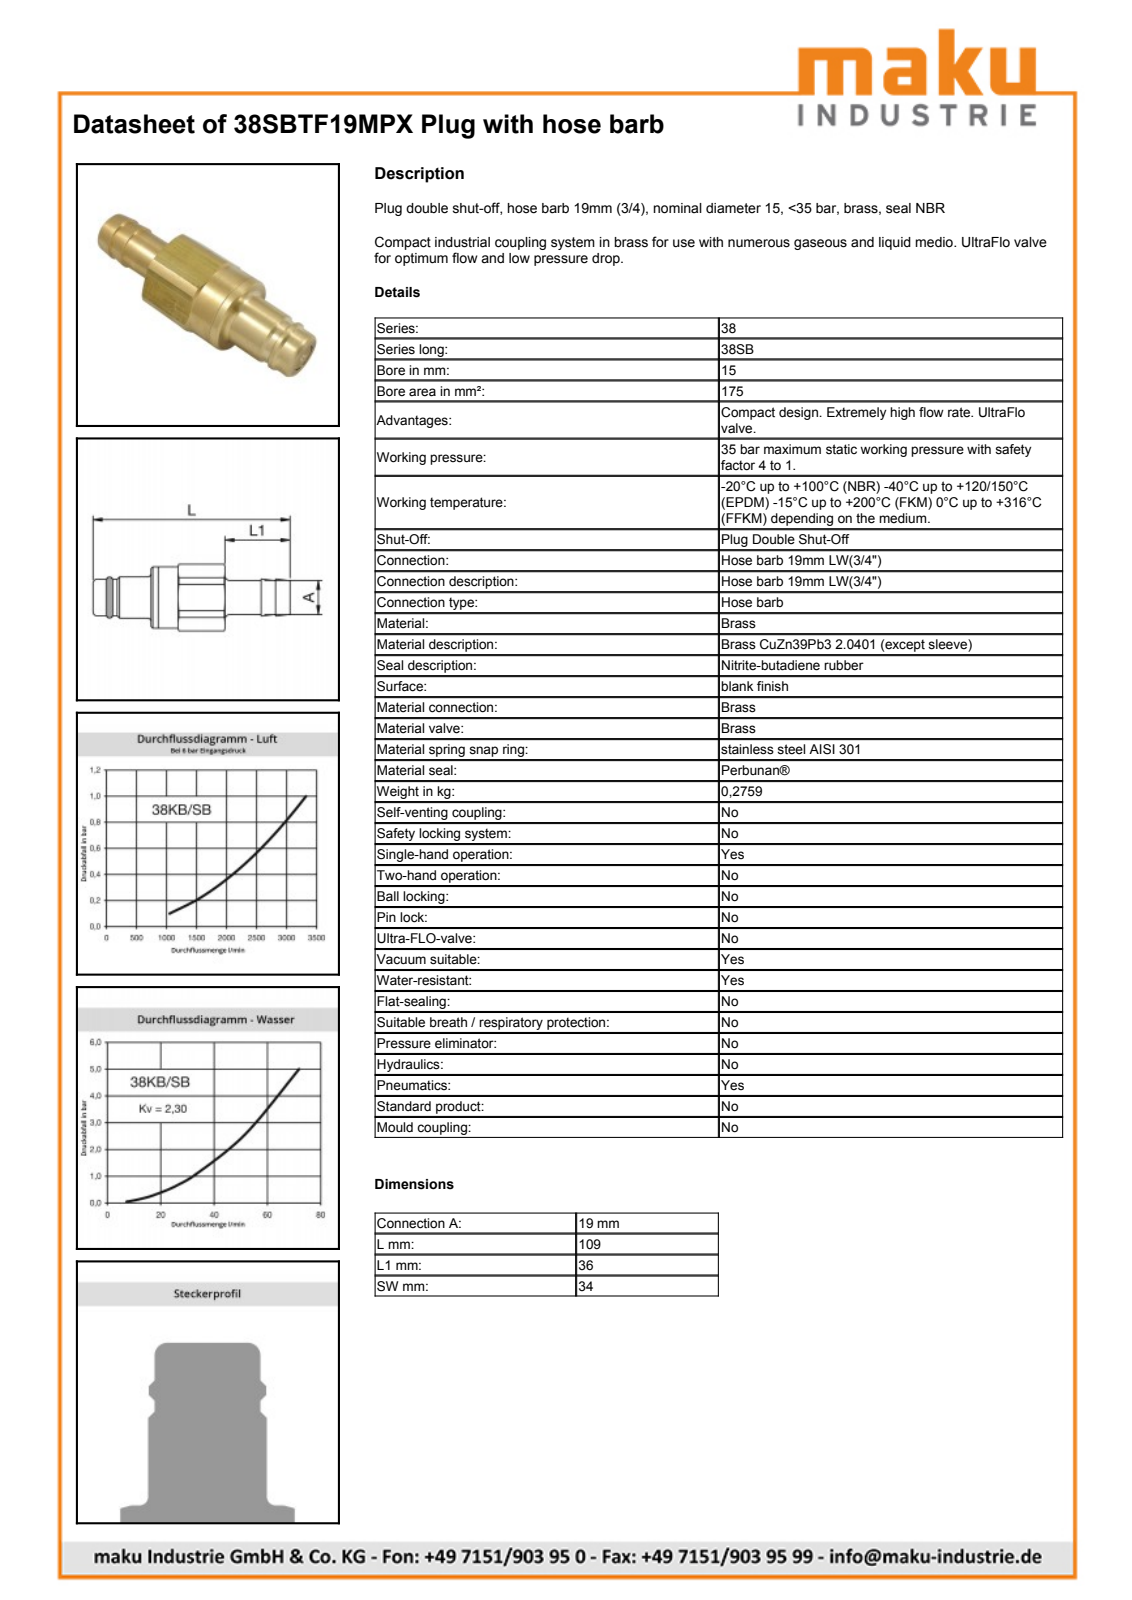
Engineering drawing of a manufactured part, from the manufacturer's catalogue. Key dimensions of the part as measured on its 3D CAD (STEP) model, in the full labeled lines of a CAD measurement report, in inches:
Part name (STEP PRODUCT): D104460
STEP written by: Autodesk Inventor 2011 (AUTOMOTIVE_DESIGN)
Units: inches
Bodies: 1 solid, 63 faces (15 planar, 18 cylindrical, 30 other)
Overall size (bounding box): 4.291 × 1.457 × 1.402
Volume: 3.731 in³ · Surface area: 19.61 in²
Round holes (diameter × count): ⌀1.181 ×1
Round bosses / shafts (diameter × count): ⌀1.339 ×1, ⌀1.122 ×1, ⌀1.088 ×1, ⌀0.9 ×1, ⌀0.89 ×1, ⌀0.799 ×1, ⌀0.748 ×1
Partial cylindrical surfaces — rounded edges, fillets, slot ends (radius × count): R0.728 ×1
Main face-to-face distances: 1.339, 1.338, 1.339, 1.417, 2.874, 1.61, 3.028, 1.264, 4.291, 1.907
